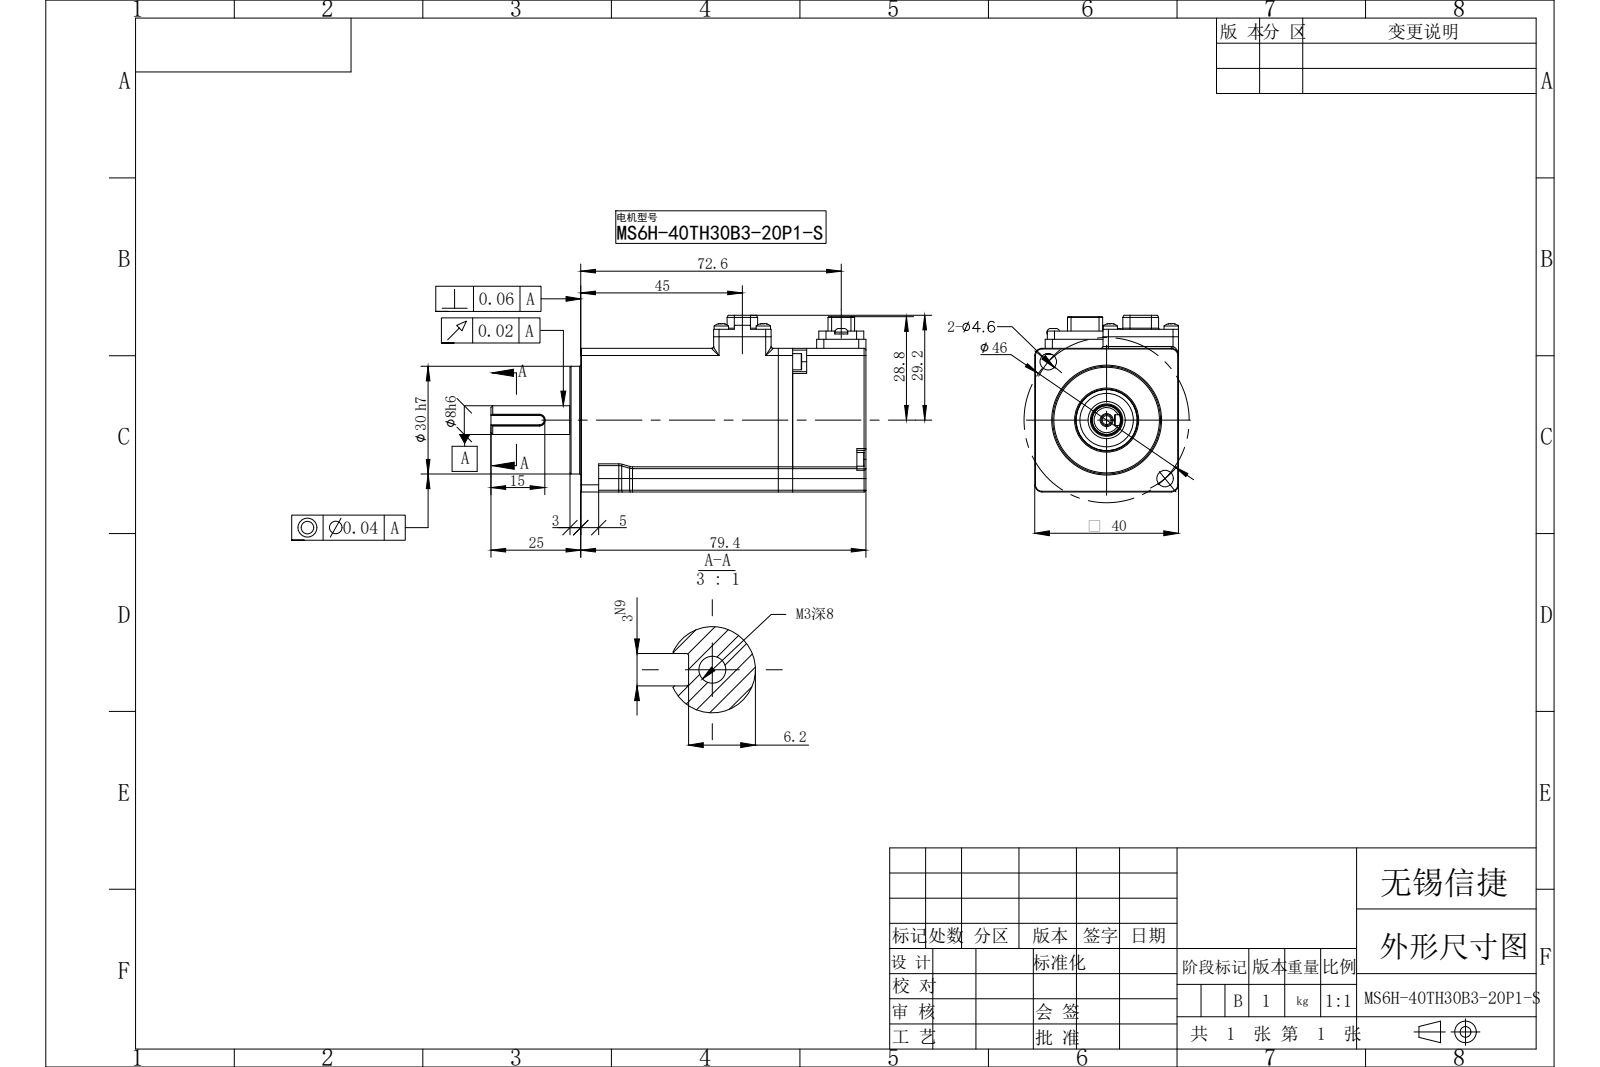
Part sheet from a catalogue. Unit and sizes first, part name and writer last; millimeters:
Units: millimetres
Overall size (bounding box): 104.4 × 49.2 × 40
Round holes (diameter × count): ⌀2.1 ×4, ⌀1.6 ×2, ⌀4.6 ×2, ⌀2.5 ×1, ⌀9 ×1, ⌀14.86 ×1
Round bosses / shafts (diameter × count): ⌀4 ×4, ⌀3.8 ×4, ⌀4.5 ×2, ⌀3.5 ×2, ⌀30 ×1, ⌀17 ×1, ⌀10.34 ×1, ⌀8.5 ×1
Partial cylindrical surfaces — rounded edges, fillets, slot ends (radius × count): R0.5 ×56, R0.2 ×18, R2 ×16, R0.3 ×10, R3 ×8, R1.5 ×5, R1 ×4, R2.5 ×4
Main face-to-face distances: 40, 6.5, 33.5, 79.4, 20.4, 59, 3, 62, 82.4, 27
Hole centre spacings: 8, 16.6, 18.43, 23, 17, 23.59, 28.08, 28.3
Bodies: 0 solids, 695 faces (369 planar, 210 cylindrical, 116 other)
Part name (STEP PRODUCT): MS6H-40TH30B3-20P1-S
STEP written by: SolidWorks 2022 (CONFIG_CONTROL_DESIGN)
